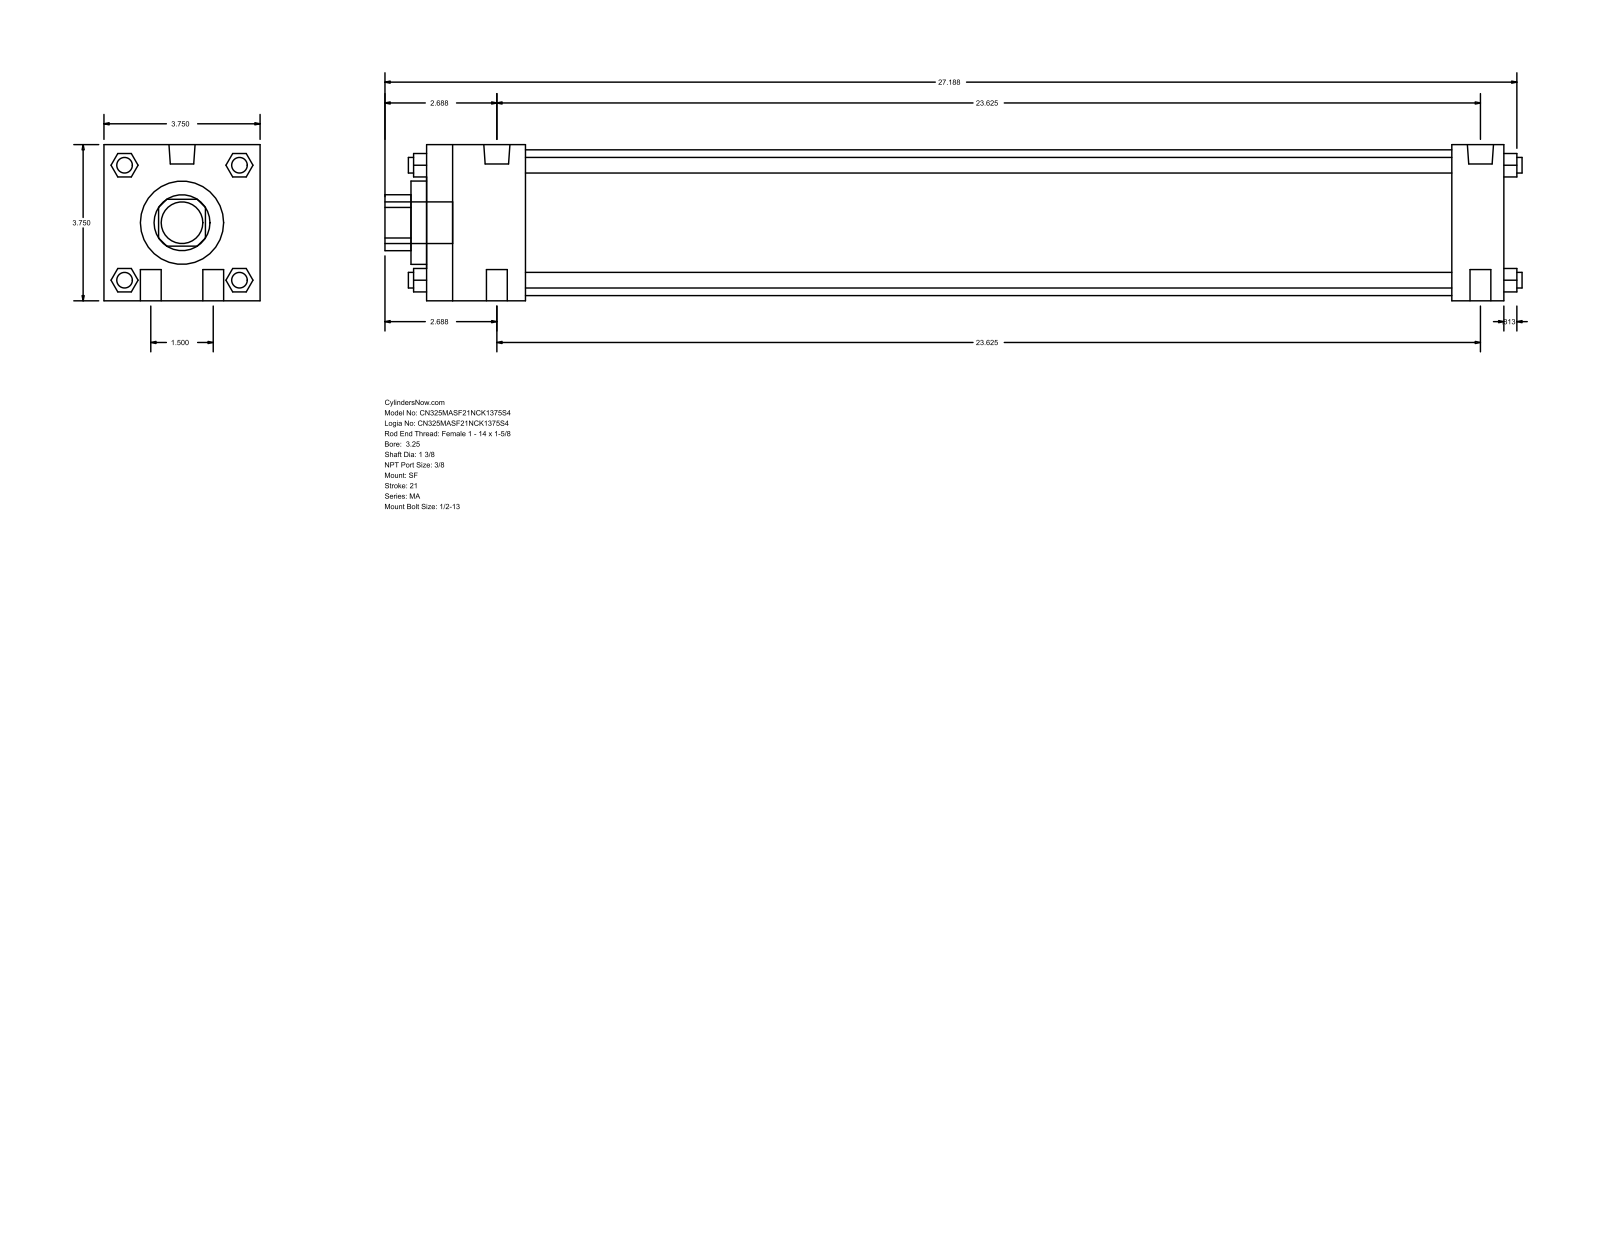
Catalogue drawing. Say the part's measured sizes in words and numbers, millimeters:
The part is named "MA_SF__0325_1.375". Its 3-D file was written by "GSSL Pune (CONFIG_CONTROL_DESIGN)". It is 0 solids with 124 faces: 94 planar, 30 cylindrical and 0 other. Overall it measures 693.74 by 95.25 by 95.25 millimeters. Round holes: 1 of diameter 34.92, 1 of diameter 50.8, 1 of diameter 88.9. Round bosses or shafts: 4 of diameter 12.7, 4 of diameter 9.53, 2 of diameter 15.93, 2 of diameter 11.11, 1 of diameter 25.4. Partial cylindrical surfaces (rounded edges, fillets, slot ends): 1 of radius 17.06. The main face-to-face distances are 95.24, 657.22, 625.48, 31.74, 60.32, 565.16, 596.9, 9.52, 69.84, 635.
